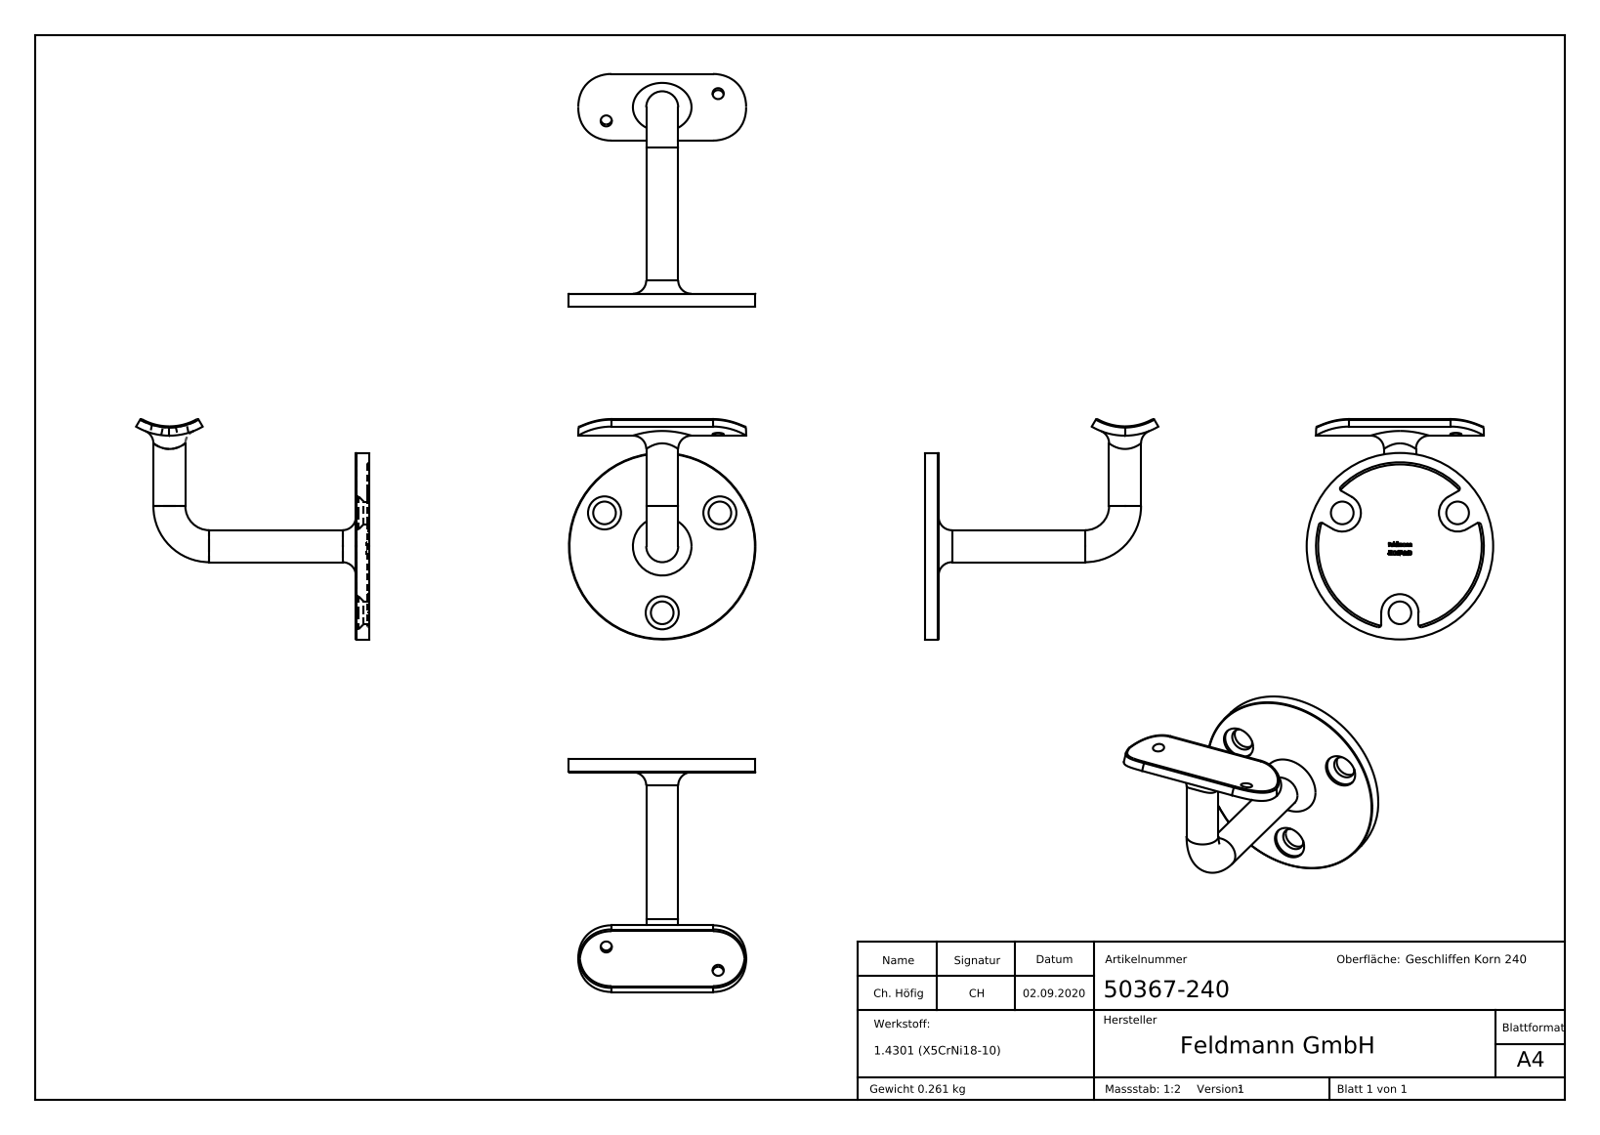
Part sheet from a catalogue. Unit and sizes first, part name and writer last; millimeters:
Units: millimetres
Overall size (bounding box): 87.5 × 82.74 × 70
Round holes (diameter × count): ⌀8.5 ×3, ⌀12.4 ×3, ⌀4.2 ×2
Round bosses / shafts (diameter × count): ⌀12 ×2, ⌀70 ×1
Partial cylindrical surfaces — rounded edges, fillets, slot ends (radius × count): R1 ×6, R12.45 ×4, R7 ×3, R0.5 ×2, R21.2 ×1, R24.7 ×1
Main face-to-face distances: 4.2, 0.8, 5, 14, 0.9, 4.1, 2.97, 0.39, 1.32, 4.09
Hole centre spacings: 43.3
Volume: 33 069 mm³ · Surface area: 15 913 mm²
Bodies: 1 solid, 298 faces (132 planar, 41 cylindrical, 125 other)
Part name (STEP PRODUCT): 50367-240
STEP written by: SolidWorks 2018 (CONFIG_CONTROL_DESIGN)
